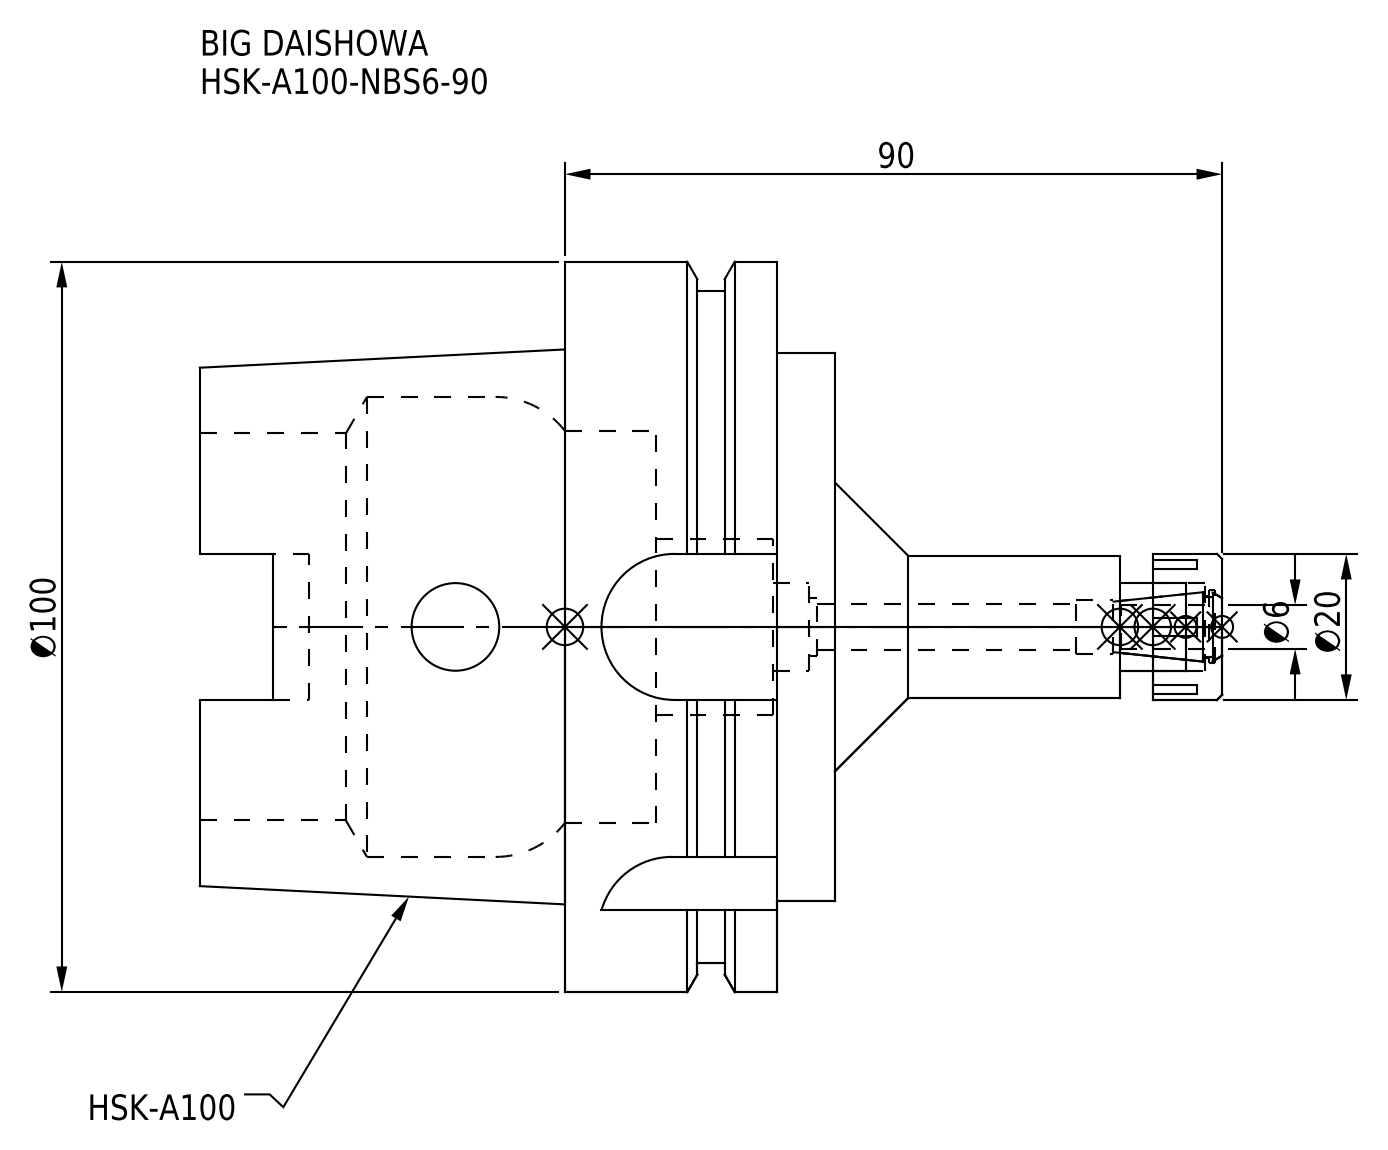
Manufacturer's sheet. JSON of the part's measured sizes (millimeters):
{"part_name": "HSK-A100-NBS6-90; HA100NB06090-060_ASM.stp; HSK-A100-NBS6-90-FreeParts; HSK-A100-NBS6-90_1.stp (+3 more)", "step_written_by": "SolidWorks 2019 (CONFIG_CONTROL_DESIGN)", "units": "millimeters", "bodies": {"solids": 2, "faces": 141, "planar": 67, "cylindrical": 52, "other": 22}, "overall_size": [140, 100, 100], "volume_mm3": 305153, "surface_area_mm2": 57178, "round_holes": [[12, 2], [6.4, 1], [7.5, 1], [8, 1], [8.5, 1], [10, 1], [24, 1], [53, 1], [53.8, 1], [63, 1]], "round_bosses_or_shafts": [[100, 1], [92, 1], [75, 1], [20, 1], [19.5, 1]], "partial_cylinders_radius": [[4.88, 4], [10, 4]], "face_to_face_distances": [37, 8, 29, 24.55, 16.55, 12.45, 87, 79, 62.45, 50]}
